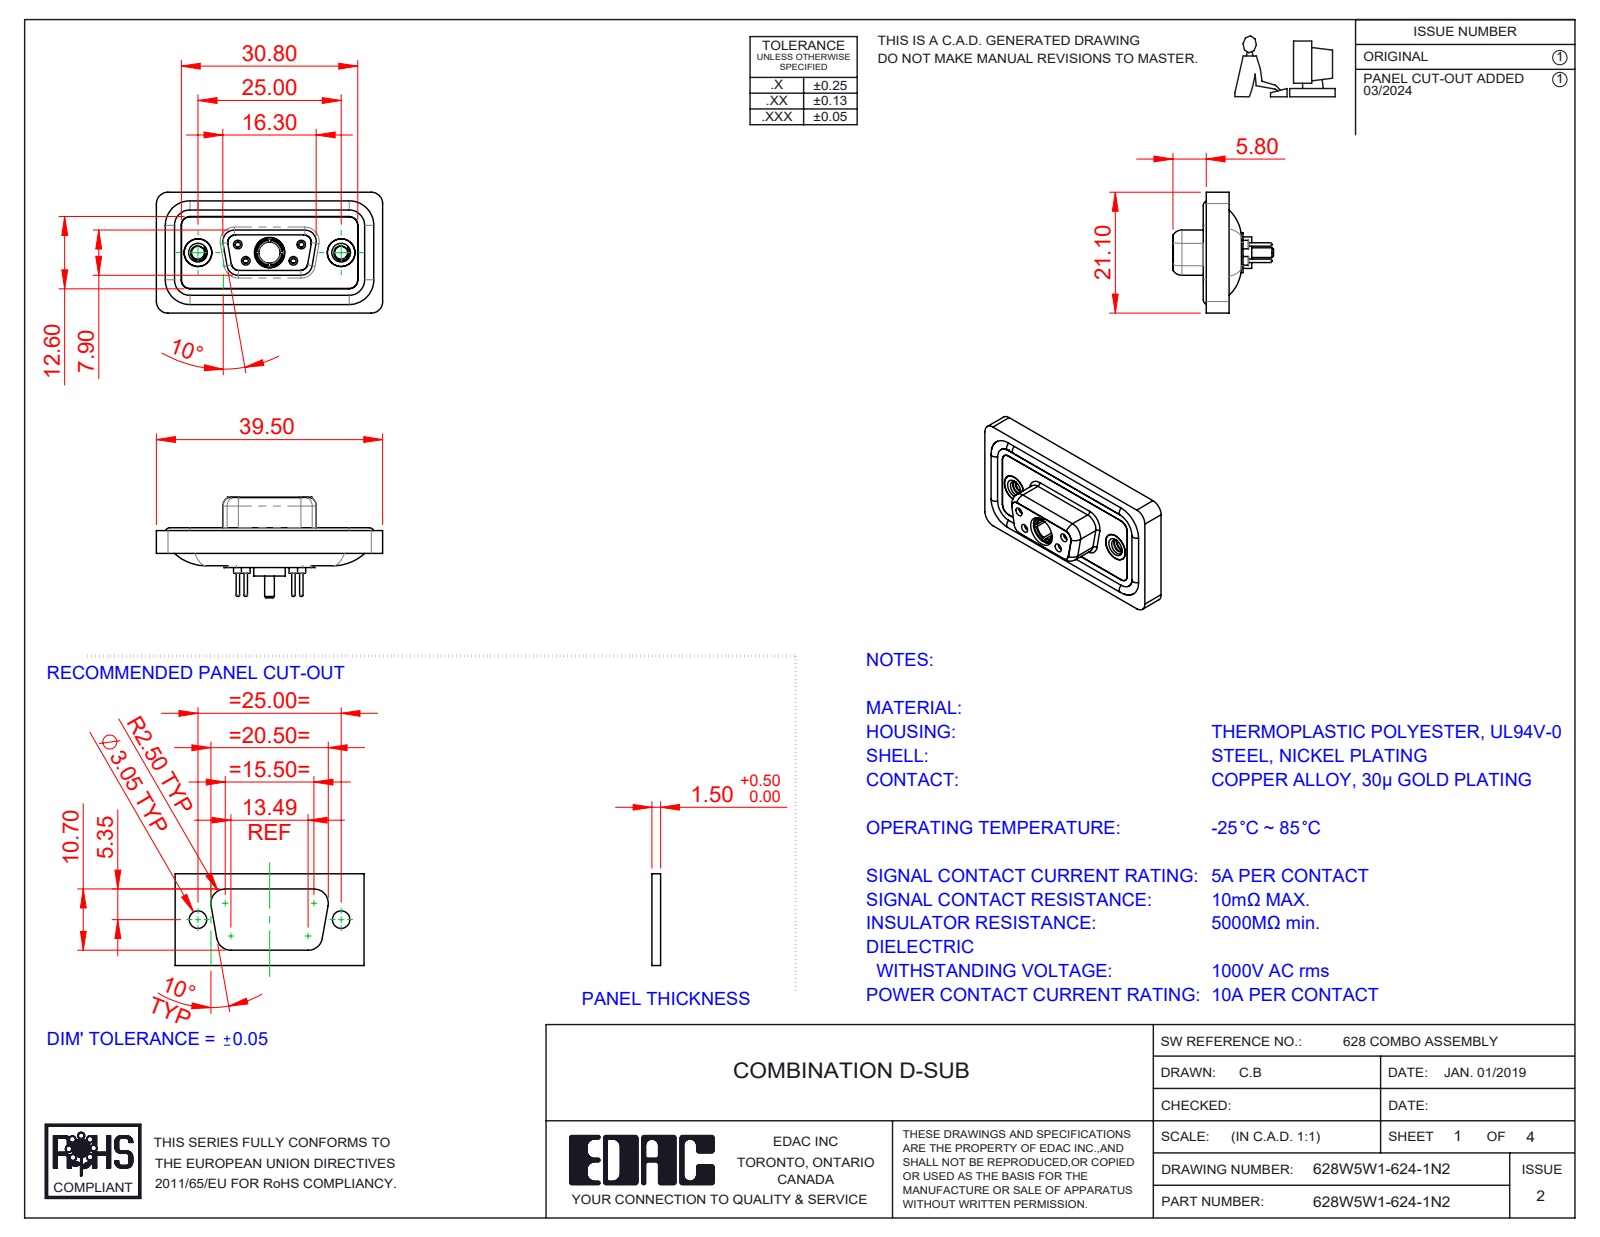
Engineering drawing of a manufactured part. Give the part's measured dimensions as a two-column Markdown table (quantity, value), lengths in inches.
| quantity | value |
| --- | --- |
| part name | 628Combo Threaded Rivet_2; 628Combo Waterproof Housing_09 Contacts; Power Socket_10A S; 628Combo Shell Rear_09 Contacts (+5 more) |
| STEP written by | SolidWorks 2023 (CONFIG_CONTROL_DESIGN) |
| units | inches |
| bodies | 13 solids, 680 faces (194 planar, 287 cylindrical, 199 other) |
| overall size | 1.555 × 0.831 × 0.691 |
| volume | 0.29 in³ |
| surface area | 11.82 in² |
| round holes (diameter × count) | 0.035 × 4, 0.043 × 4, 0.059 × 4, 0.079 × 4, 0.191 × 3, 0.063 × 2, 0.067 × 2, 0.089 × 2, 0.157 × 2, 0.159 × 2, 0.197 × 2, 0.146 × 1 |
| round bosses / shafts (diameter × count) | 0.063 × 6, 0.087 × 4, 0.024 × 4, 0.195 × 2, 0.189 × 2, 0.217 × 1, 0.205 × 1, 0.195 × 1 |
| partial cylindrical surfaces (radius × count) | 0.059 × 22, 0.079 × 18, 0.053 × 8, 0.063 × 8, 0.01 × 4, 0.02 × 4, 0.024 × 4, 0.026 × 4 |
| main face-to-face distances | 0.016, 0.114, 0.071, 0.043, 0.063, 0.02, 0.222, 0.293, 0.211, 0.26 |
| hole center spacings | 0.124, 0.225, 0.28, 0.492, 0.713, 0.173, 0.173, 0.327 |
